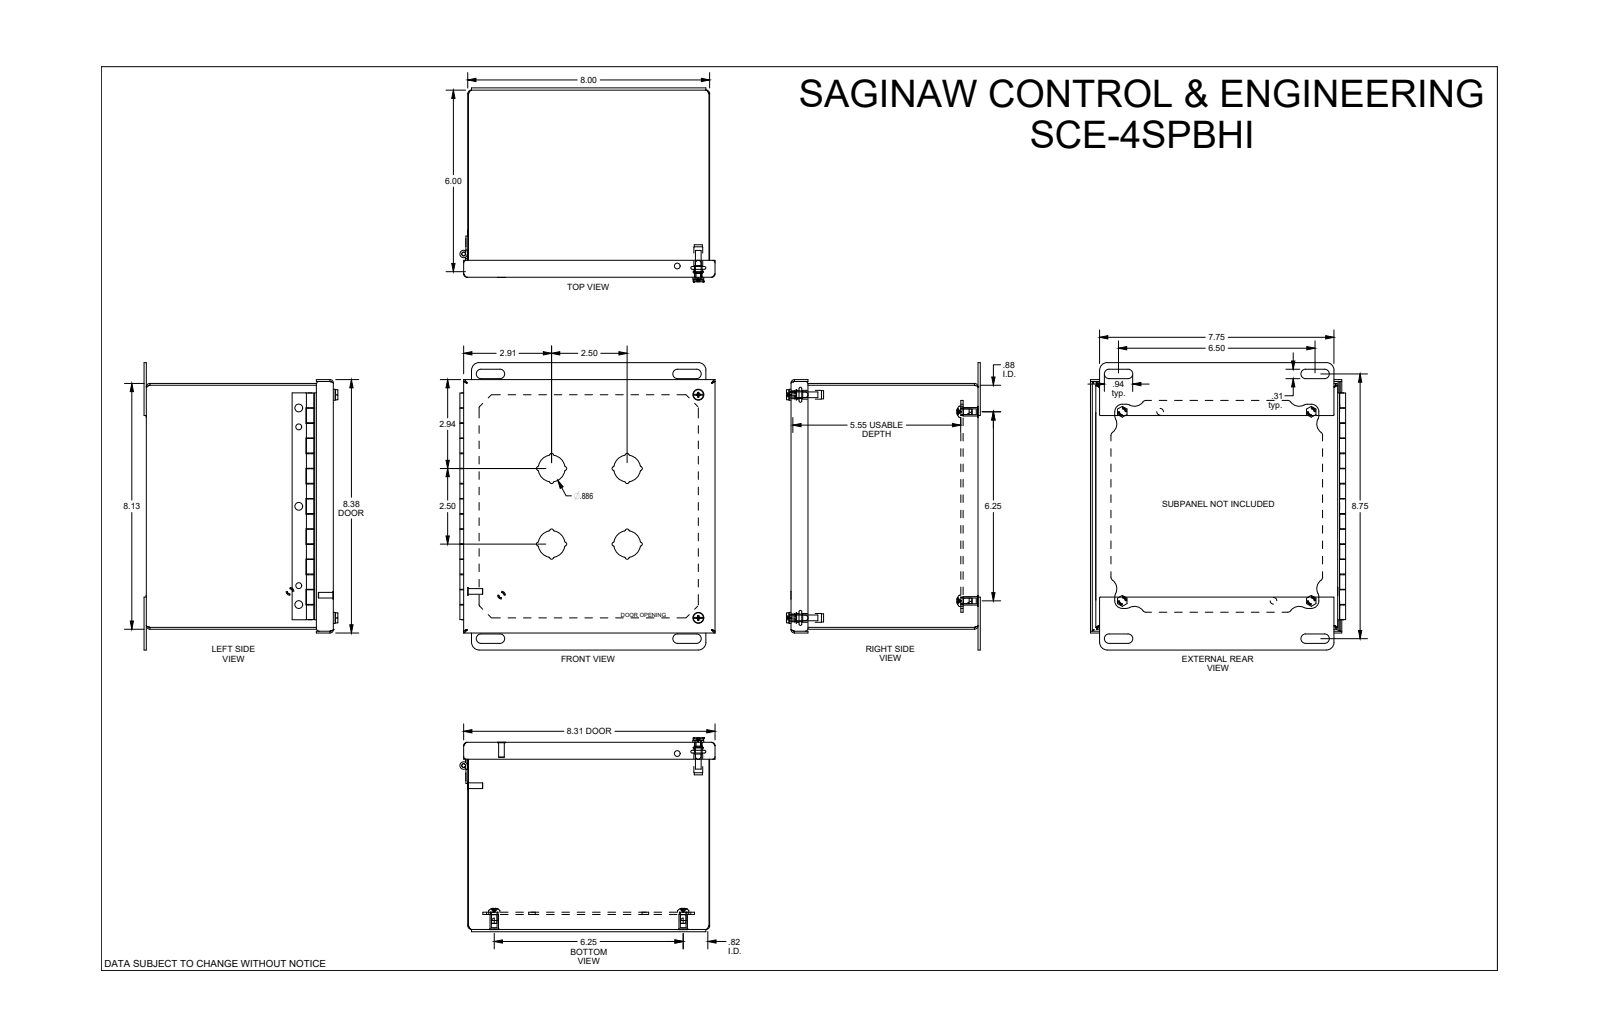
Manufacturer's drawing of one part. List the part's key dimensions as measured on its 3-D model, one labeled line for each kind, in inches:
Part name (STEP PRODUCT): SCE-4SPBHI
STEP written by: SolidWorks 2021 (AUTOMOTIVE_DESIGN)
Units: inches
Bodies: 7 solids, 817 faces (329 planar, 336 cylindrical, 152 other)
Overall size (bounding box): 9.5 × 8.438 × 6.323
Volume: 29.42 in³ · Surface area: 884.5 in²
Round holes (diameter × count): ⌀0.19 ×9, ⌀0.25 ×6, ⌀0.266 ×4, ⌀0.317 ×4, ⌀0.126 ×2, ⌀0.193 ×2, ⌀0.218 ×2, ⌀0.22 ×2
Round bosses / shafts (diameter × count): ⌀0.188 ×5, ⌀0.28 ×4, ⌀0.256 ×4, ⌀0.362 ×2, ⌀0.292 ×2, ⌀0.27 ×2, ⌀0.26 ×2, ⌀0.246 ×2
Partial cylindrical surfaces — rounded edges, fillets, slot ends (radius × count): R0.04 ×32, R0.06 ×20, R0.01 ×18, R0.062 ×16, R0.25 ×16, R0.125 ×8, R0.156 ×8, R0.344 ×8
Main face-to-face distances: 0.06, 6.125, 7.94, 0.06, 6.065, 6.185, 0.075, 0.435, 0.51, 0.495
Hole centre spacings: 0.753, 7.25, 9.59, 6.773, 6.831, 7.229, 0.037, 0.625
